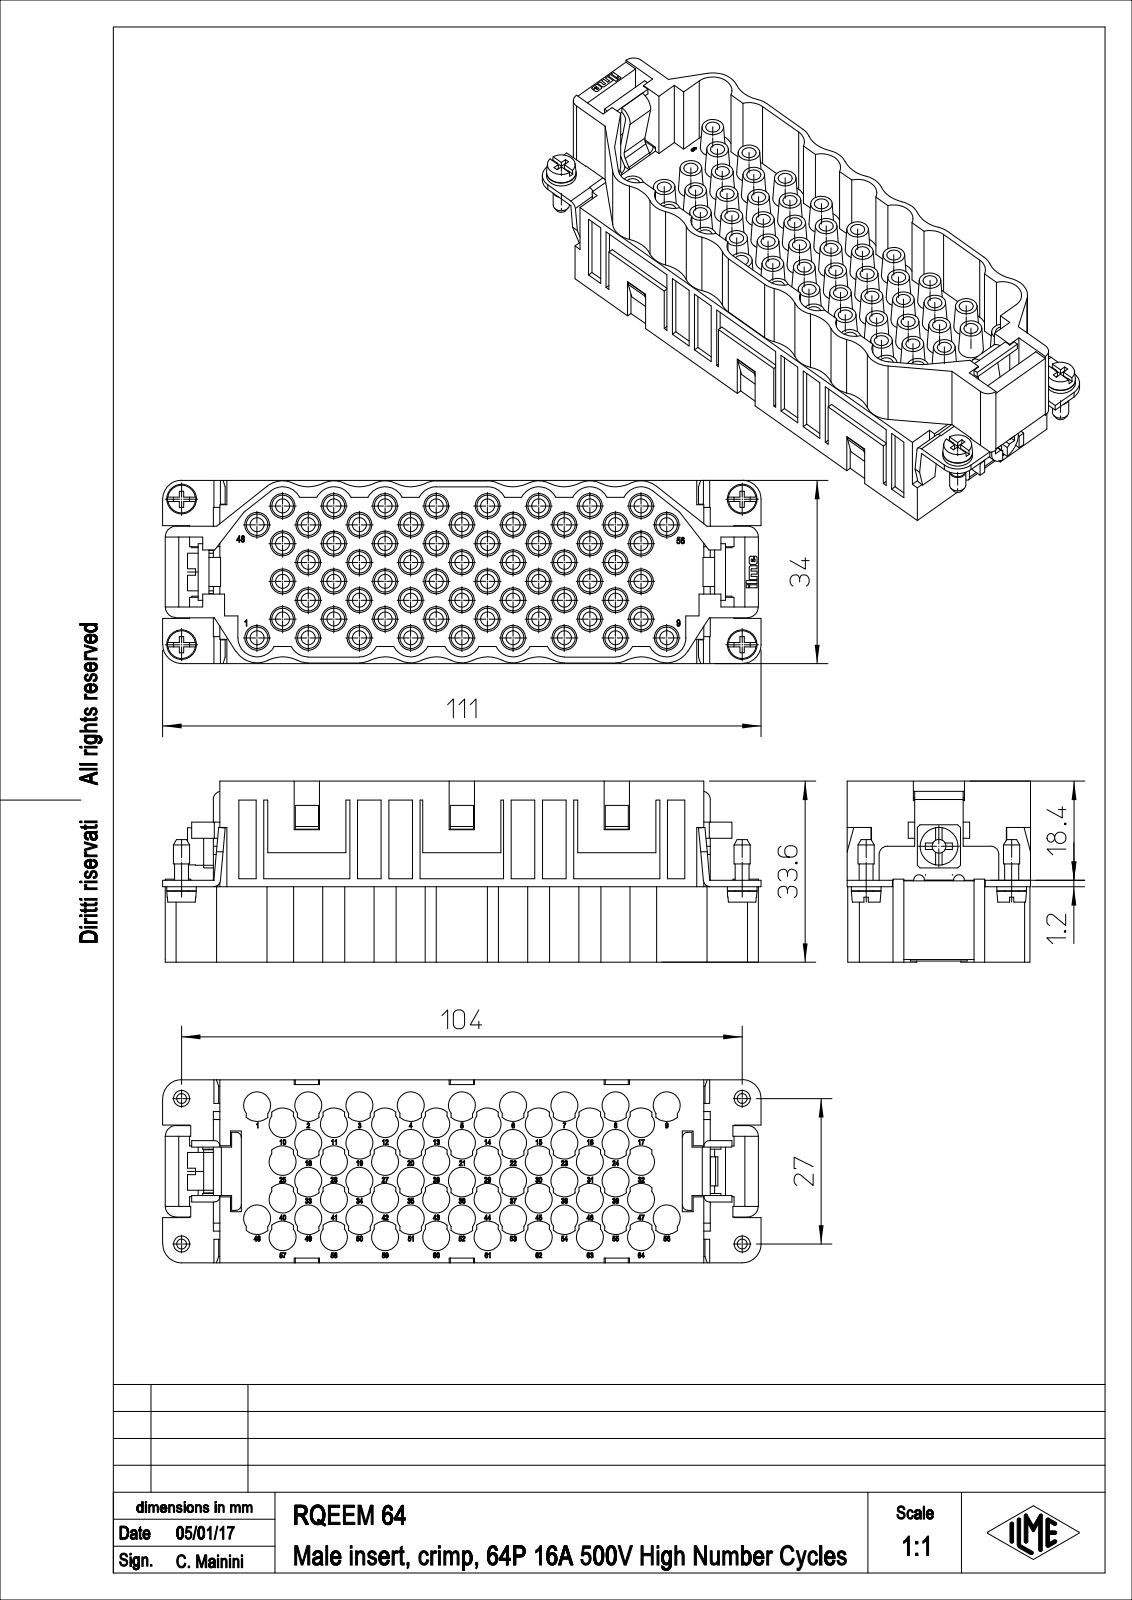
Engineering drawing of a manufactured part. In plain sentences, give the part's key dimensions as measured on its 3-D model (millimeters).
The part is named "RQEEM_64". Its 3-D file was written by "PTC Creo Elements/Direct Modeling 19.0E 27-Jun-2016 (C) Parametric Technology GmbH (AUTOMOTIVE_DESIGN)". It is 1 solid with 1991 faces: 1057 planar, 660 cylindrical and 274 other. Overall it measures 111 by 34 by 33.6 millimeters. Its volume is 59 124 cubic millimeters and its surface area 39 520 square millimeters. Round holes: 64 of diameter 2.6, 64 of diameter 5, 4 of diameter 2.8, 1 of diameter 2.58, 1 of diameter 3. Round bosses or shafts: 4 of diameter 5.5, 4 of diameter 3, 4 of diameter 2.6, 1 of diameter 7, 1 of diameter 6. Partial cylindrical surfaces (rounded edges, fillets, slot ends): 64 of radius 3, 17 of radius 3.55, 17 of radius 4.65, 12 of radius 1, 12 of radius 6.16, 6 of radius 2, 4 of radius 1.2, 4 of radius 1.5. The main face-to-face distances are 15, 18.6, 1.2, 3, 33.1, 0.9, 12, 15.6, 3.6, 34. The hole center spacings are 5.9, 11.8, 11.52, 20.25, 24.01, 14.67, 17.7, 33.43.
